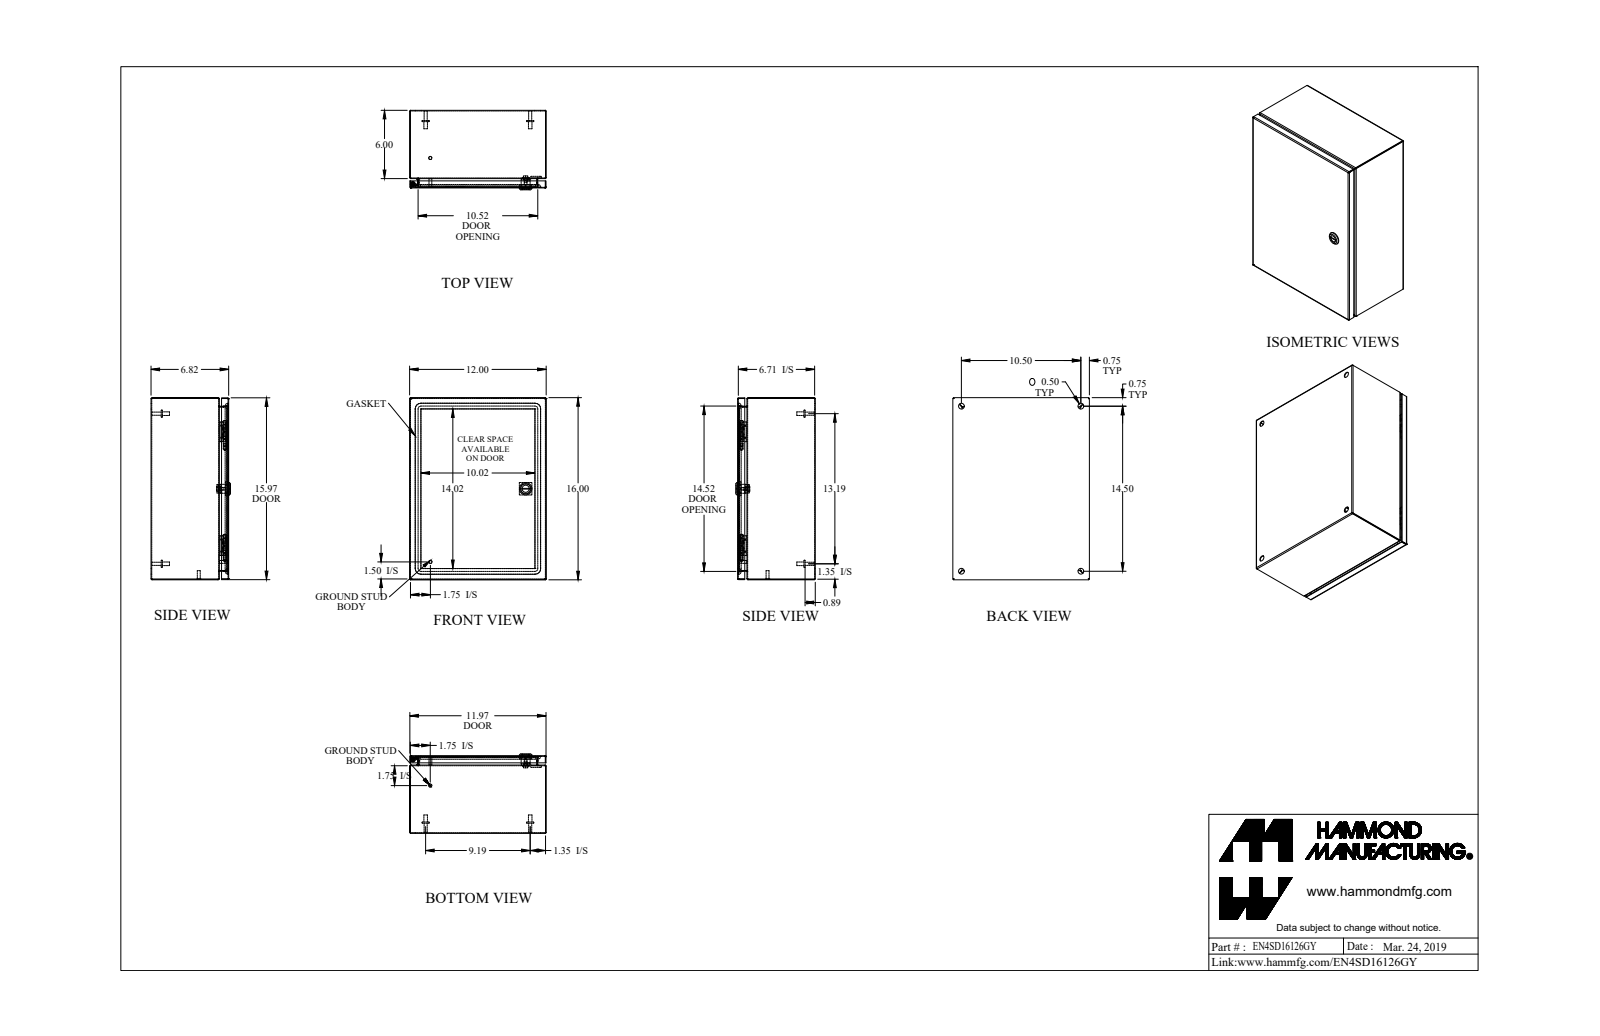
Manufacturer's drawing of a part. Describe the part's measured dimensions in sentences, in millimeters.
The part is named "EN4SD16126GY_Default". Its 3-D file was written by "SolidWorks 2019 (CONFIG_CONTROL_DESIGN)". It is 21 solids with 634 faces: 285 planar, 213 cylindrical and 136 other. Overall it measures 406.4 by 304.8 by 177.3 millimeters. Its volume is 868 800 cubic millimeters and its surface area 1 152 000 square millimeters. Round holes: 4 of diameter 12.7, 1 of diameter 4.4, 1 of diameter 5.9, 1 of diameter 6.1, 1 of diameter 6.1, 1 of diameter 15.9, 1 of diameter 19.9. Round bosses or shafts: 4 of diameter 15.9, 4 of diameter 8, 4 of diameter 6.9, 2 of diameter 7.1, 2 of diameter 6.4, 1 of diameter 27.9, 1 of diameter 13.3, 1 of diameter 11.6. Partial cylindrical surfaces (rounded edges, fillets, slot ends): 21 of radius 0.7, 21 of radius 2.2, 16 of radius 6.4, 8 of radius 482.6, 4 of radius 0.2, 4 of radius 1.6, 4 of radius 12.7, 2 of radius 3.2. The main face-to-face distances are 1.4, 171.8, 170.4, 173.3, 303.4, 405, 301.9, 304.8, 403.5, 406.4. The hole center spacings are 266.7, 368.3, 454.7, 186.1, 186.1, 302.3, 302.4.
